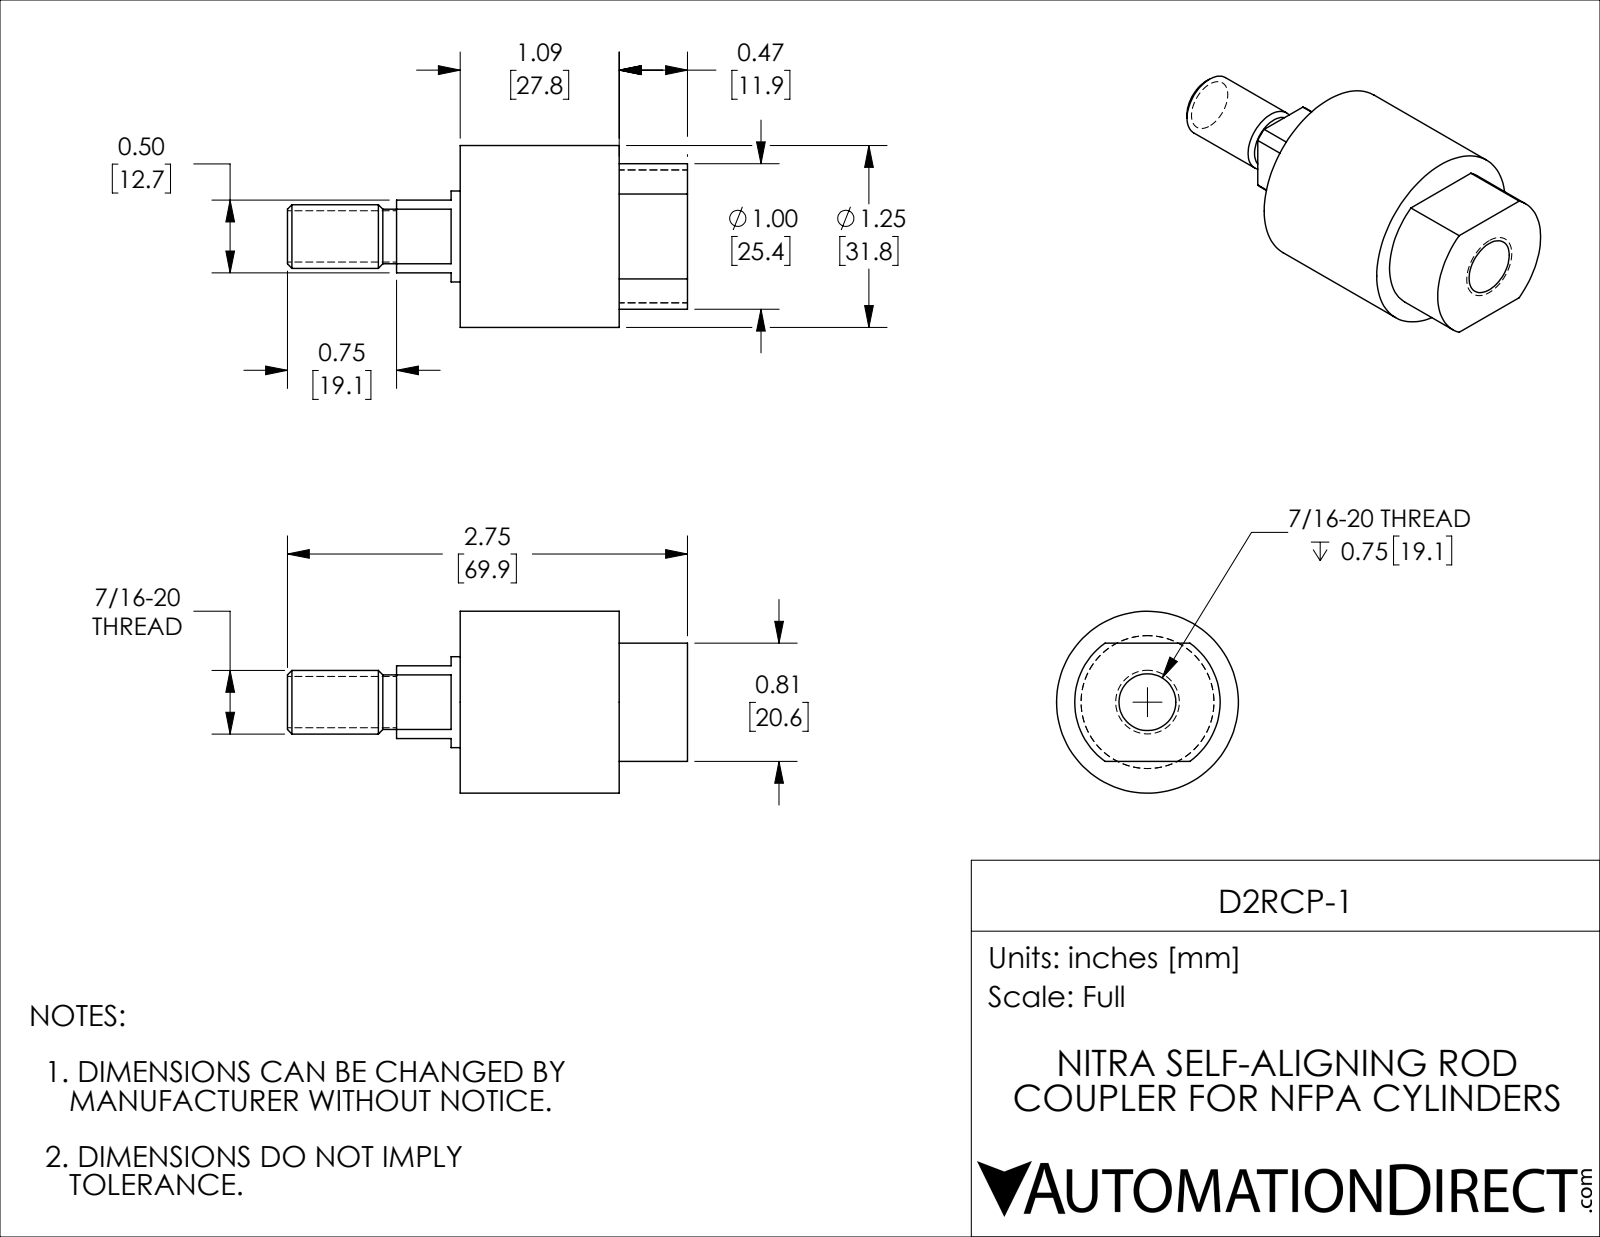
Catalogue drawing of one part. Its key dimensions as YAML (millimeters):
part_name: "D2RCP-1"
step_written_by: "SolidWorks 2019 (CONFIG_CONTROL_DESIGN)"
units: millimeters
bodies: {solids: 1, faces: 34, planar: 15, cylindrical: 13, other: 6}
overall_size: [69.9, 31.8, 31.8]
volume: 28990
surface_area: 7284
round_holes:
  - {diameter: 9.9, count: 1}
round_bosses_or_shafts:
  - {diameter: 31.8, count: 1}
  - {diameter: 15.9, count: 1}
  - {diameter: 11.1, count: 1}
  - {diameter: 9.5, count: 1}
partial_cylinders:
  - {radius: 12.7, count: 1}
face_to_face_distances: [39.7, 11.9, 27.8, 4, 16.7, 12.7, 20.7, 50.8, 38.9, 11.1]
